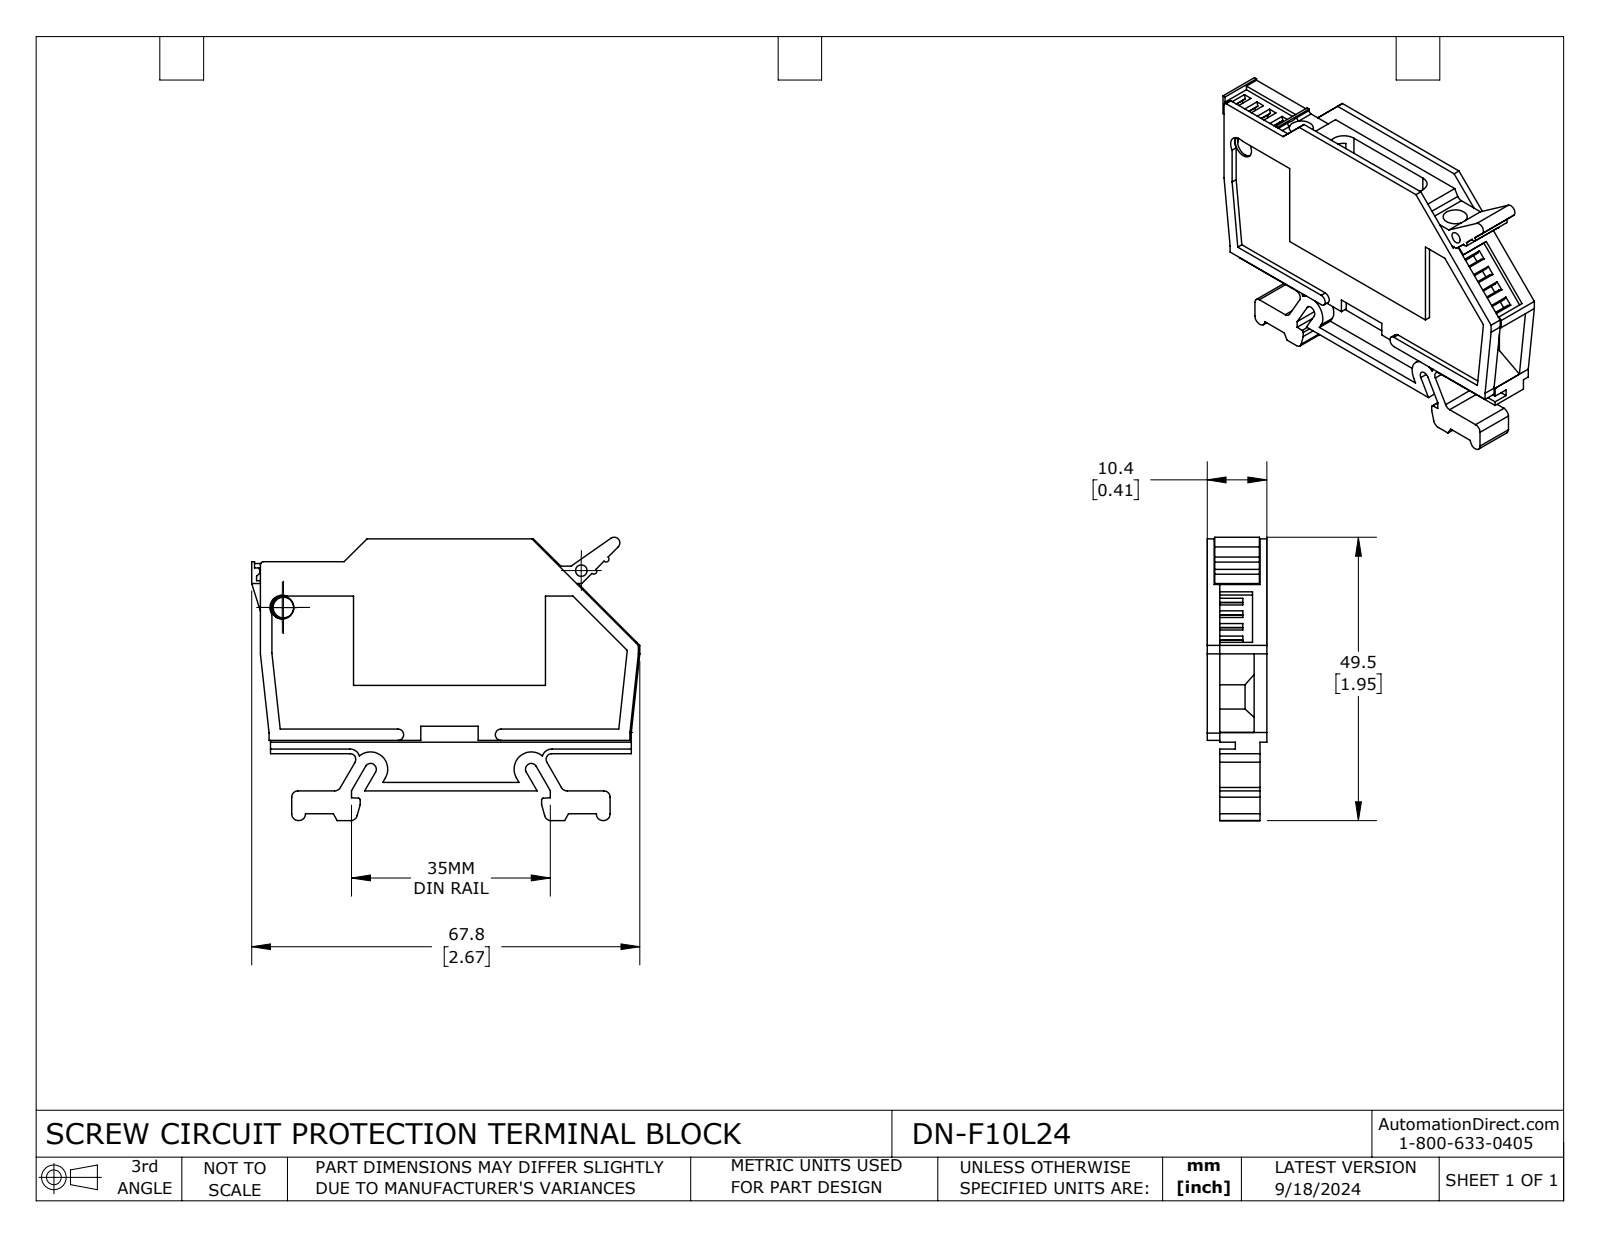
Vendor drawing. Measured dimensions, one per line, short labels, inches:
name: DN-F10L24
written by: SolidWorks 2023 (CONFIG_CONTROL_DESIGN)
unit: in
bodies: 1 solid, 440 faces (292 planar, 78 cylindrical, 70 other)
size: 2.669 × 1.948 × 0.409
volume: 0.902 in³; area: 21.57 in²
holes: 3× ⌀0.165, 2× ⌀0.079, 1× ⌀0.098, 1× ⌀0.157
bosses: 1× ⌀0.157
rounds: 12× R0.039, 6× R0.047, 4× R0.02, 3× R0.049, 3× R0.079, 2× R0.012, 2× R0.043, 2× R0.071
face distances: 0.047, 0.039, 0.358, 0.323, 0.362, 0.087, 0.311, 0.079, 0.051, 0.319
hole spacings: 0.826, 0.828, 1.496, 2.064, 2.072, 2.151
